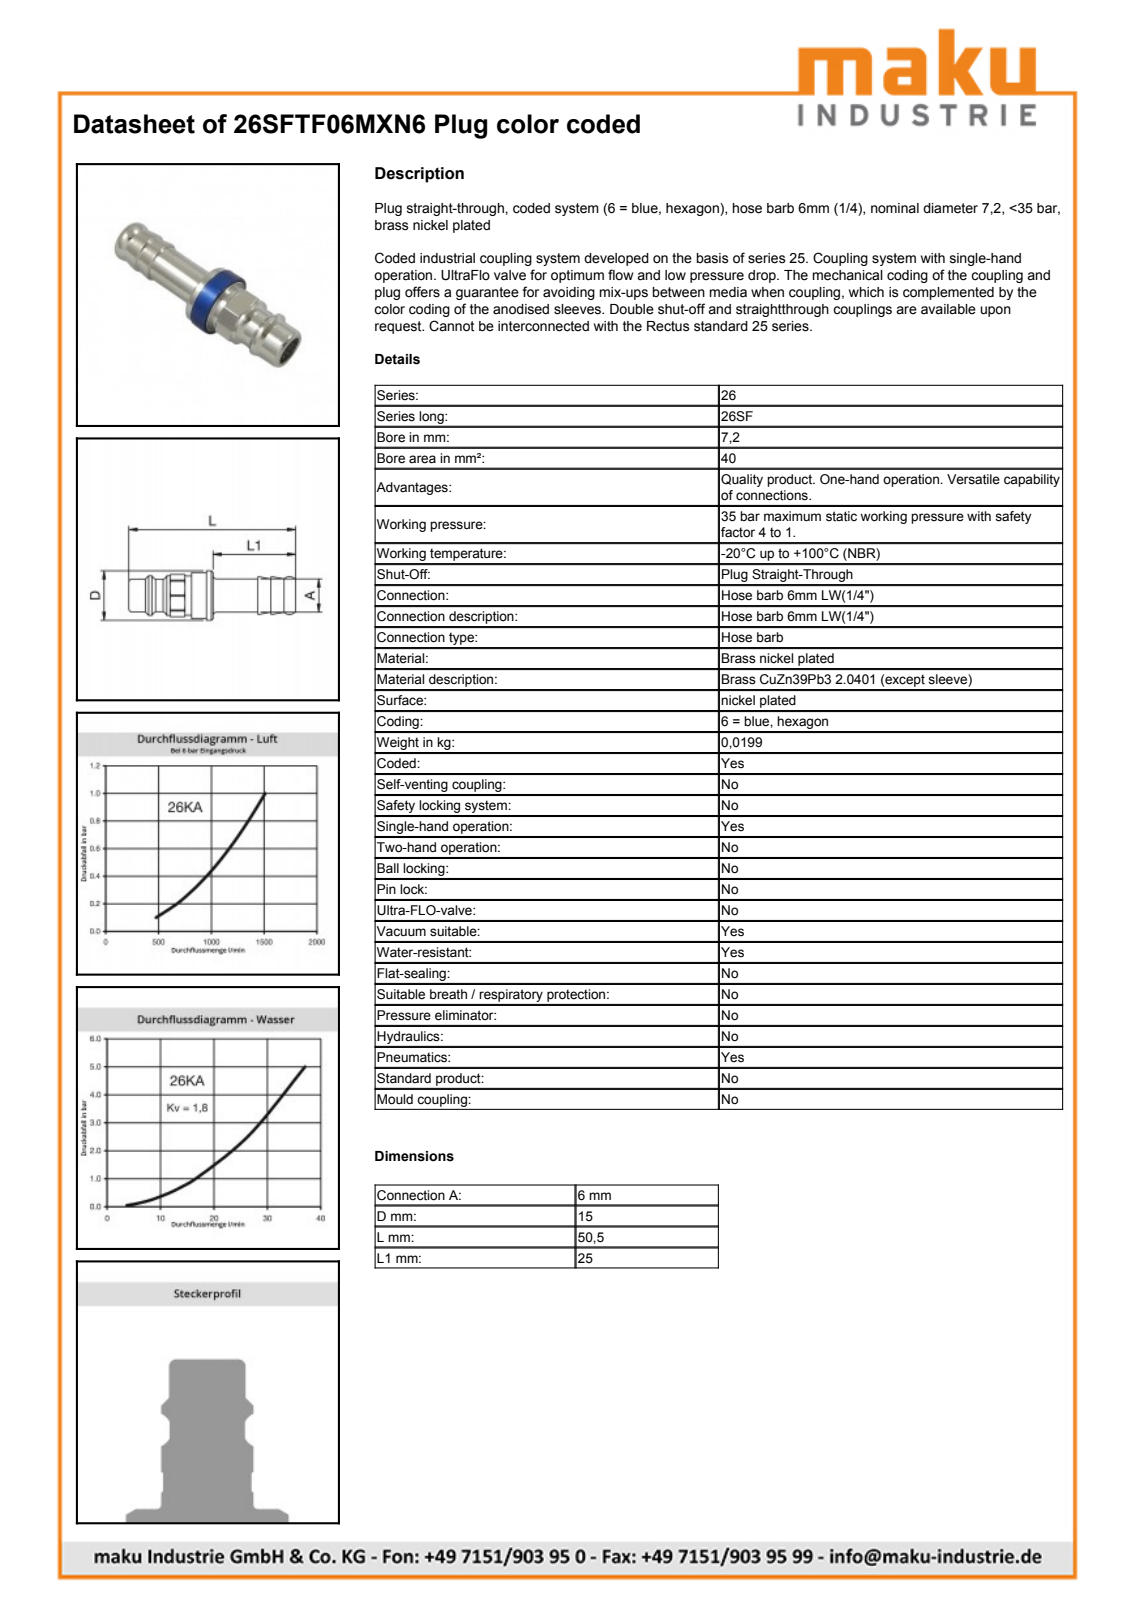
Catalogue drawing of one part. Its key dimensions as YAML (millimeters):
part_name: "D103820; D103816; D103012"
step_written_by: "Autodesk Inventor 2011 (AUTOMOTIVE_DESIGN)"
units: millimeters
bodies: {solids: 2, faces: 63, planar: 15, cylindrical: 19, other: 29}
overall_size: [50.5, 15.5, 15.5]
volume: 2396
surface_area: 3173
round_holes:
  - {diameter: 4.1, count: 1}
  - {diameter: 7.85, count: 1}
  - {diameter: 13.85, count: 1}
  - {diameter: 14.05, count: 1}
round_bosses_or_shafts:
  - {diameter: 15.5, count: 1}
  - {diameter: 15, count: 1}
  - {diameter: 14, count: 1}
  - {diameter: 12, count: 1}
  - {diameter: 11.9, count: 1}
  - {diameter: 10, count: 1}
  - {diameter: 9.75, count: 1}
  - {diameter: 6.1, count: 1}
partial_cylinders:
  - {radius: 6.8, count: 1}
face_to_face_distances: [12, 2, 6.5, 4.5, 6.2, 4.2, 25, 27, 31.2, 31.5]
